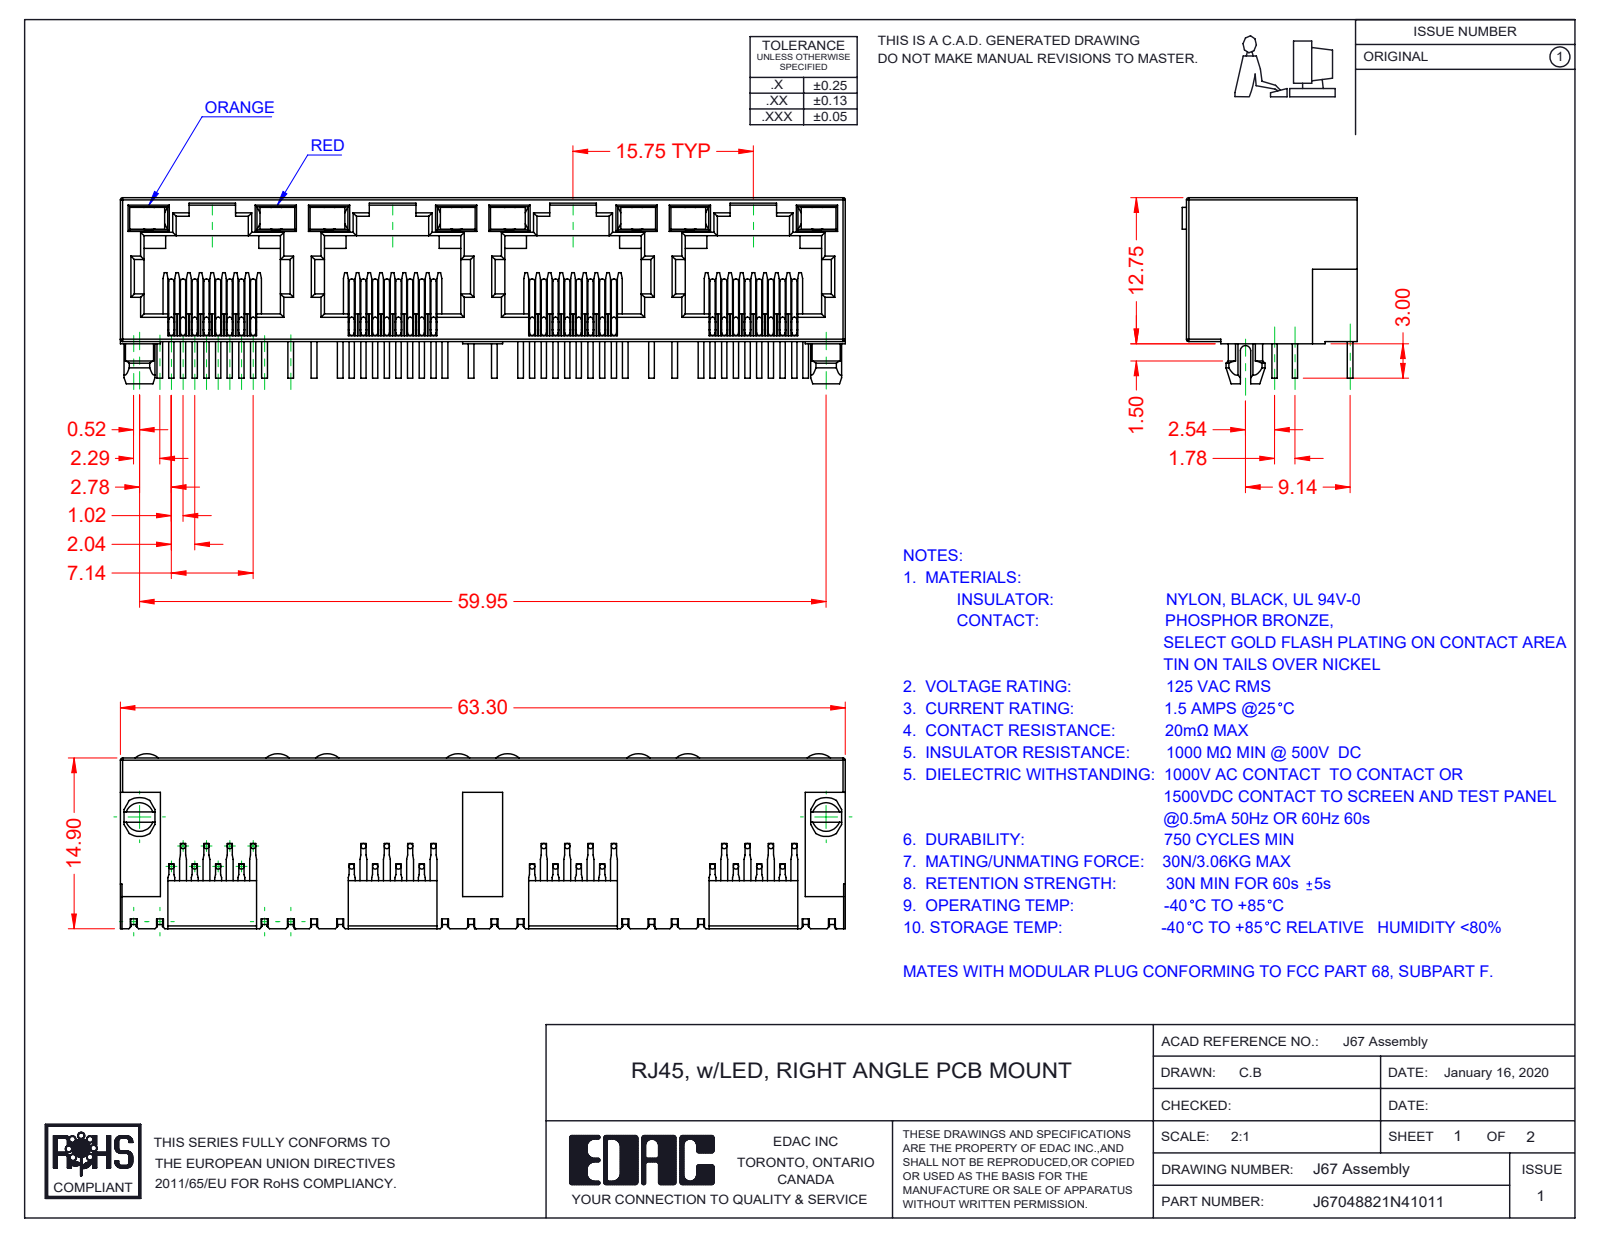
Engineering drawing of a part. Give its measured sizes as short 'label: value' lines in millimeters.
name: 67 Insulator; 67 LED RH_2-Red; 67 Contacts; J67048822N42011 (+1 more)
written by: SolidWorks 2016 (CONFIG_CONTROL_DESIGN)
unit: mm
bodies: 41 solids, 2465 faces (1781 planar, 476 cylindrical, 208 other)
size: 63.3 × 16.25 × 15.28
volume: 5 159 mm³; area: 11 573 mm²
bosses: 96× ⌀0.46
rounds: 66× R0.2, 29× R0.3, 9× R0.45, 8× R1.55, 2× R1.5, 2× R1.7, 1× R0.35, 1× R1
face distances: 0.5, 12.55, 1.89, 0.89, 10, 15.75, 1, 1.39, 11, 11.89
